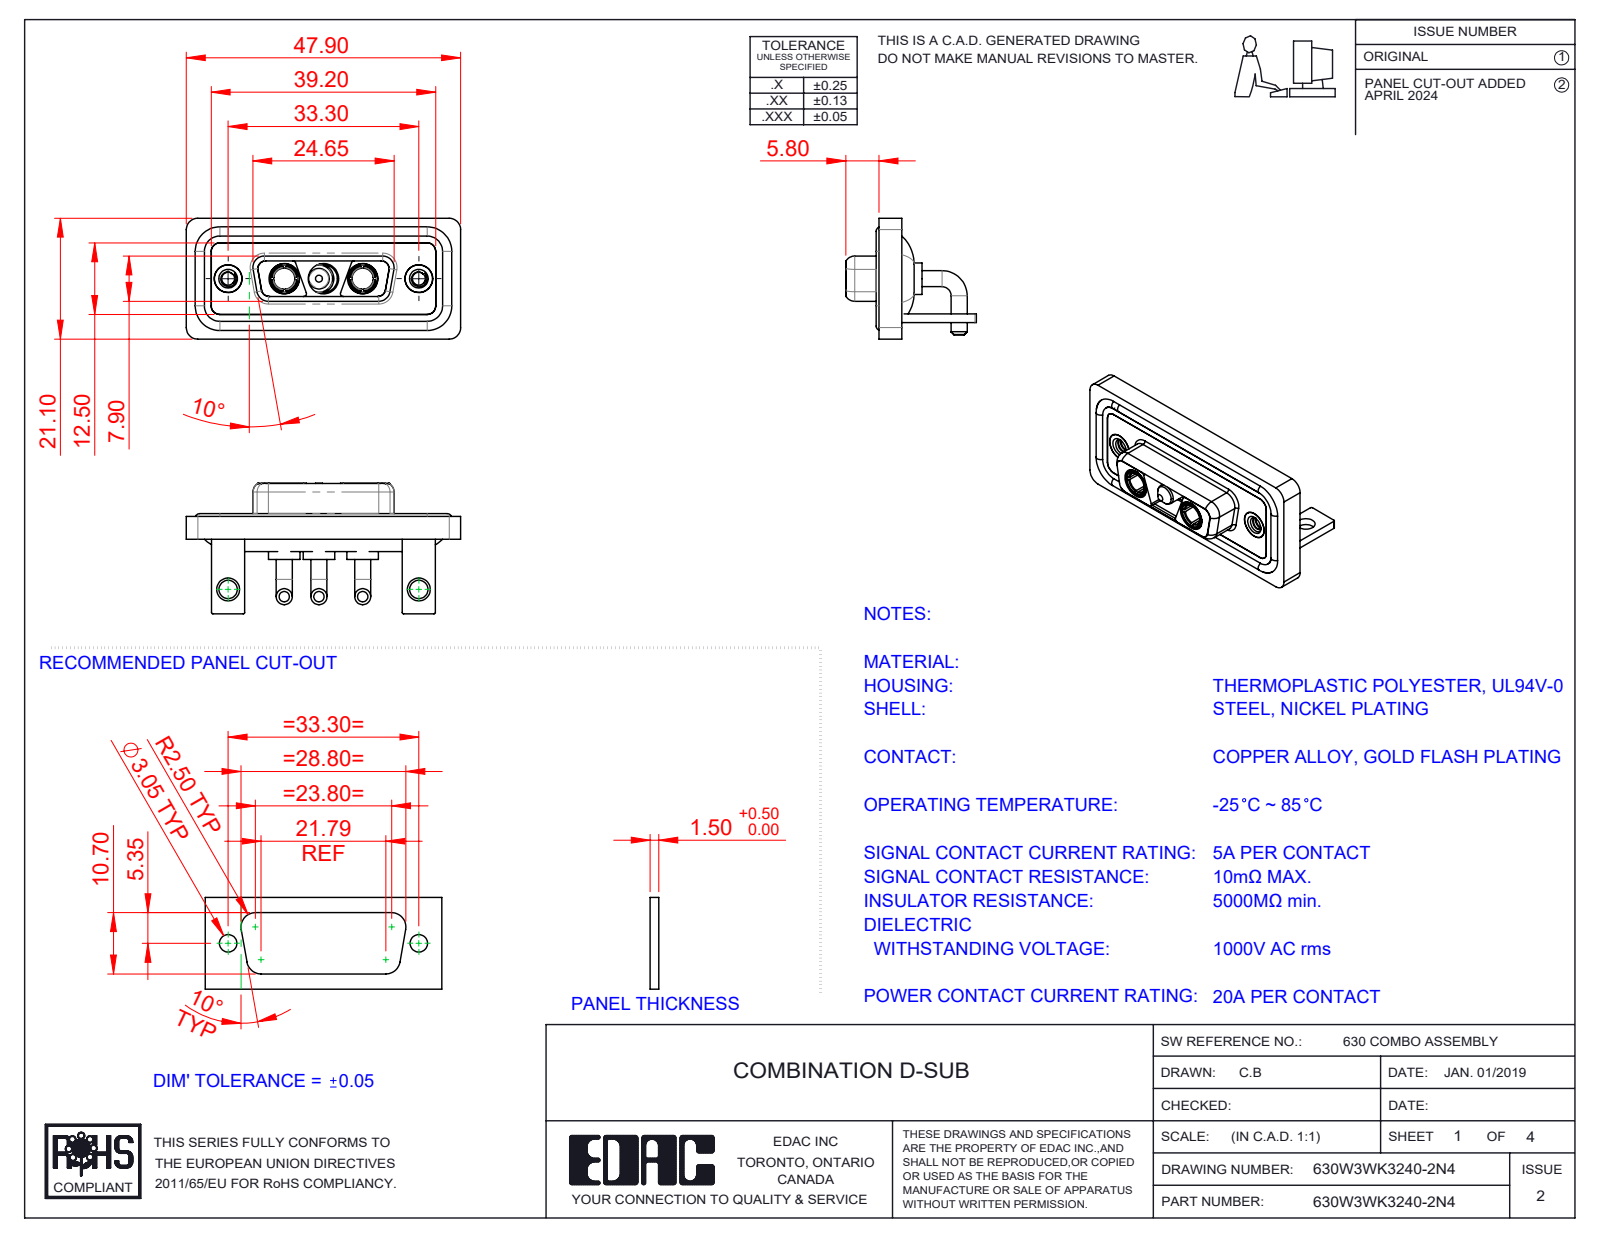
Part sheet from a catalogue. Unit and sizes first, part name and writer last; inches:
Units: inches
Overall size (bounding box): 1.886 × 0.898 × 0.831
Round holes (diameter × count): ⌀0.191 ×5, ⌀0.209 ×3, ⌀0.089 ×2, ⌀0.126 ×2, ⌀0.146 ×2, ⌀0.157 ×2, ⌀0.159 ×2, ⌀0.197 ×2
Round bosses / shafts (diameter × count): ⌀0.11 ×6, ⌀0.063 ×4, ⌀0.217 ×3, ⌀0.205 ×3, ⌀0.187 ×3, ⌀0.148 ×3, ⌀0.195 ×2, ⌀0.195 ×2
Partial cylindrical surfaces — rounded edges, fillets, slot ends (radius × count): R0.079 ×21, R0.059 ×18, R0.01 ×16, R0.053 ×12, R0.02 ×9, R0.063 ×8, R0.024 ×4, R0.026 ×4
Main face-to-face distances: 0.016, 0.114, 0.059, 0.146, 0.071, 0.043, 0.161, 0.063, 0.098, 0.055
Hole centre spacings: 0.27, 0.386, 0.656, 0.925, 1.311, 0.539
Volume: 0.39 in³ · Surface area: 16.23 in²
Bodies: 15 solids, 643 faces (198 planar, 288 cylindrical, 157 other)
Part name (STEP PRODUCT): 630Combo Housing_3WK3; Power Pin_20A RA; 630Combo Shell Front_15 Contacts; Power Socket_20A RA (+5 more)
STEP written by: SolidWorks 2023 (CONFIG_CONTROL_DESIGN)
